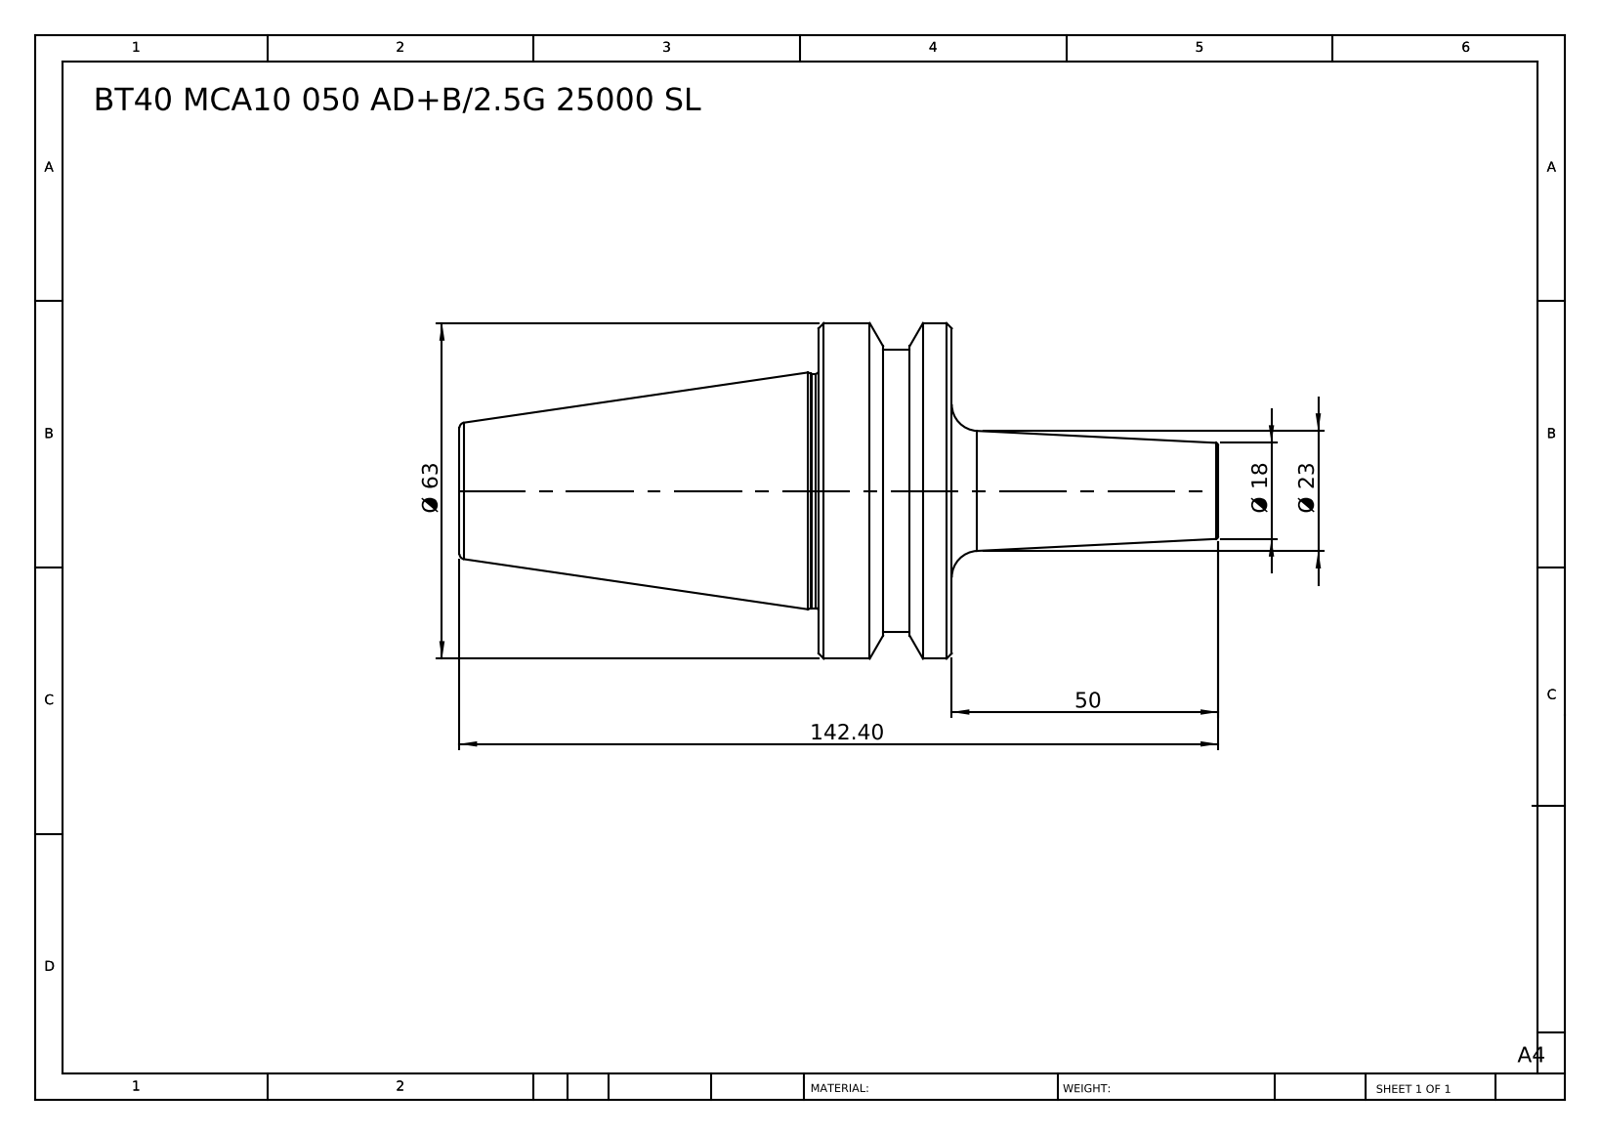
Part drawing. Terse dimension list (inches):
name: BT40 MCA10 050 AD+B-2.5G 25000 SL
written by: SolidWorks 2014 (CONFIG_CONTROL_DESIGN)
unit: in
bodies: 1 solid, 38 faces (6 planar, 8 cylindrical, 24 other)
size: 5.606 × 2.48 × 2.48
volume: 9.477 in³; area: 32.95 in²
bosses: 1× ⌀2.48, 1× ⌀2.087, 1× ⌀1.732
face distances: 0.984, 3.638, 2.654, 1.969, 2.953, 5.606, 2.476, 0.508, 0.476, 3.13
